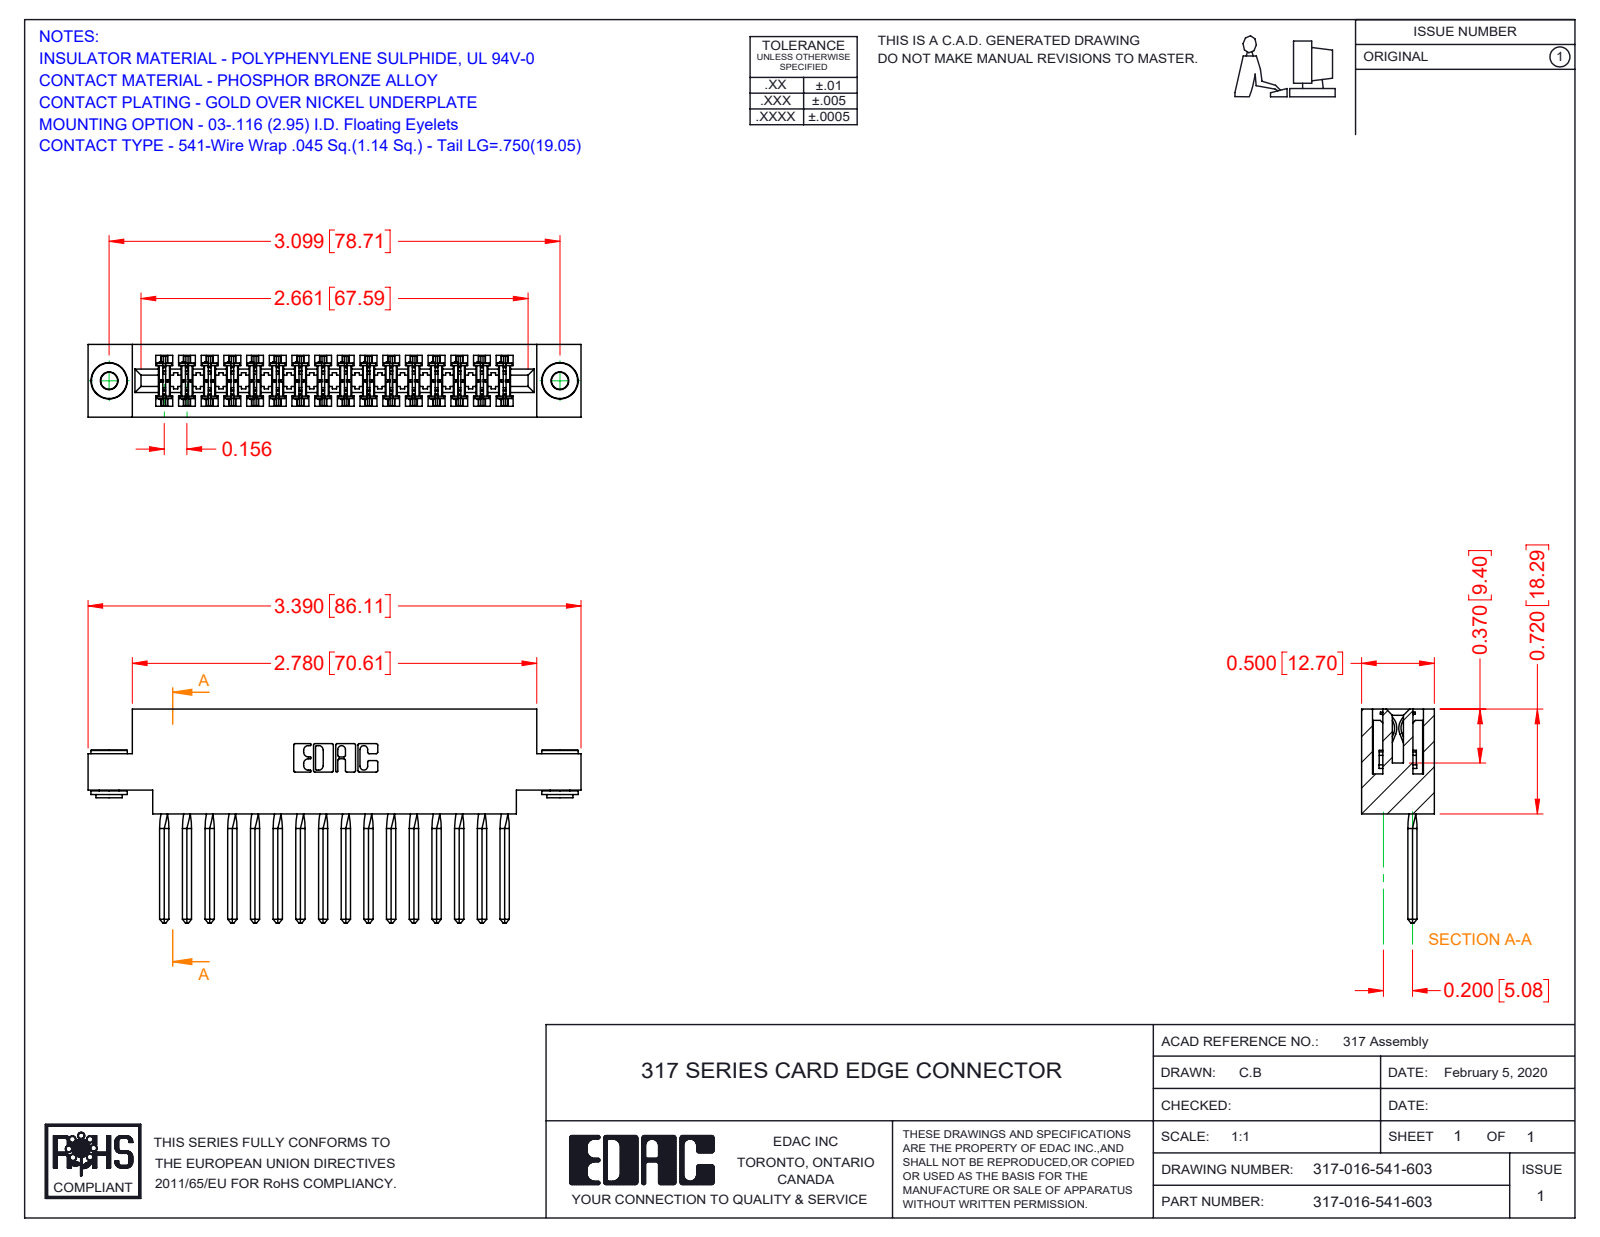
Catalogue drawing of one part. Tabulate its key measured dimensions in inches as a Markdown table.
| quantity | value |
| --- | --- |
| part name | 317 Part_.156 Dia - TH; 317-016-541-603; 317-290-002_541; 345-250-002_345-250-002-102 |
| STEP written by | SolidWorks 2016 (CONFIG_CONTROL_DESIGN) |
| units | inches |
| bodies | 19 solids, 2572 faces (2052 planar, 448 cylindrical, 72 other) |
| overall size | 3.39 × 1.47 × 0.5 |
| volume | 0.805 in³ |
| surface area | 27.86 in² |
| round holes (diameter × count) | 0.116 × 2, 0.156 × 2 |
| round bosses / shafts (diameter × count) | 0.25 × 2, 0.18 × 2, 0.136 × 2 |
| partial cylindrical surfaces (radius × count) | 0.015 × 32, 0.01 × 22, 0.007 × 6, 0.031 × 6, 0.026 × 3, 0.095 × 2, 0.1 × 2, 0.11 × 2 |
| main face-to-face distances | 0.5, 0.075, 0.425, 0.11, 0.35, 0.22, 0.195, 0.065, 0.305, 0.72 |
| hole center spacings | 3.099 |
